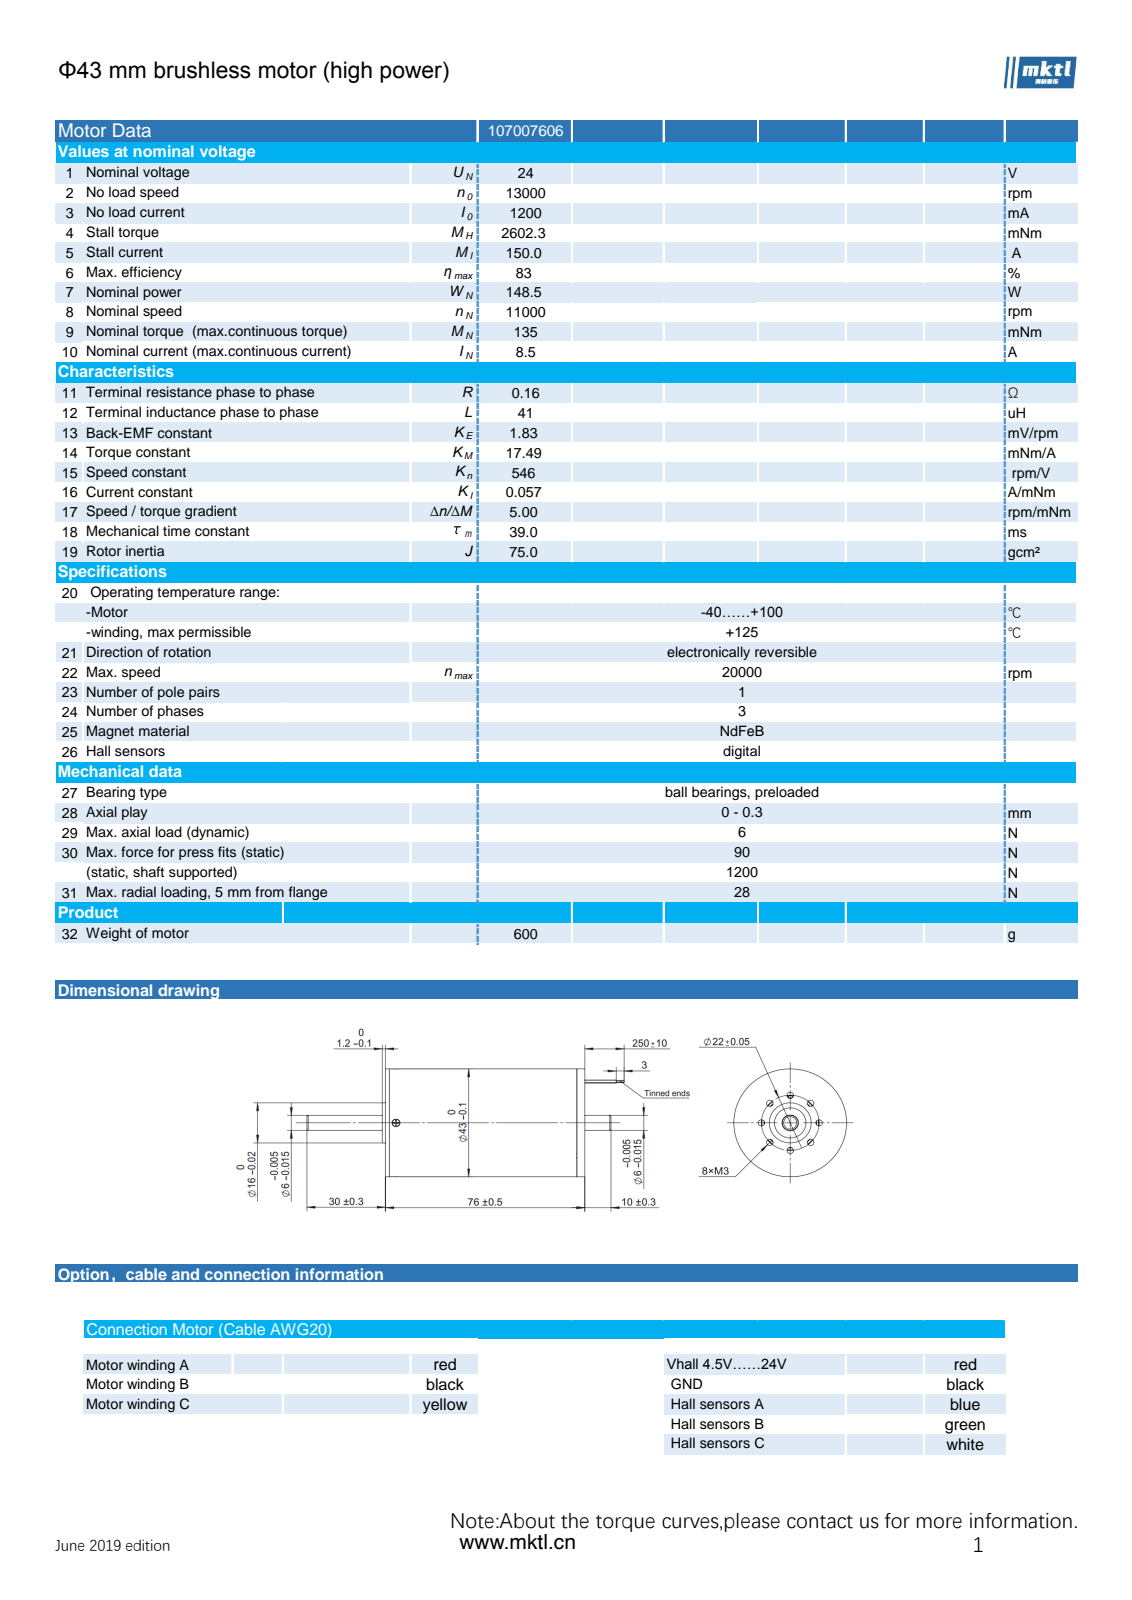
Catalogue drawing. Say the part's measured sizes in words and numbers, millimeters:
The part is named "107007606". Its 3-D file was written by "SolidWorks 2025 (AUTOMOTIVE_DESIGN)". It is 336 solids with 3050 faces: 1137 planar, 1789 cylindrical and 124 other. Overall it measures 121 by 43 by 43 millimeters. Its volume is 102 644 cubic millimeters and its surface area 445 818 square millimeters. Round holes: 9 of diameter 1, 8 of diameter 1.5, 8 of diameter 2.5, 5 of diameter 0.85, 5 of diameter 1.2, 3 of diameter 2.1, 3 of diameter 2.2, 3 of diameter 3, 2 of diameter 3.1, 1 of diameter 6, 1 of diameter 10.5, 1 of diameter 12. Round bosses or shafts: 5 of diameter 0.6, 3 of diameter 4, 3 of diameter 1.6, 3 of diameter 0.8, 3 of diameter 0.5, 2 of diameter 2.8, 2 of diameter 1.4, 2 of diameter 1.3. Partial cylindrical surfaces (rounded edges, fillets, slot ends): 24 of radius 0.1, 21 of radius 1, 3 of radius 0.3, 2 of radius 0.5, 1 of radius 2, 1 of radius 6.1, 1 of radius 6.6, 1 of radius 7.15. The main face-to-face distances are 0.4, 0.6, 0.8, 1, 1.2, 1.4, 1.6, 1.8, 2, 2.2. The hole center spacings are 8.42, 11, 15.56, 20.33, 2, 26.4, 6, 16.
